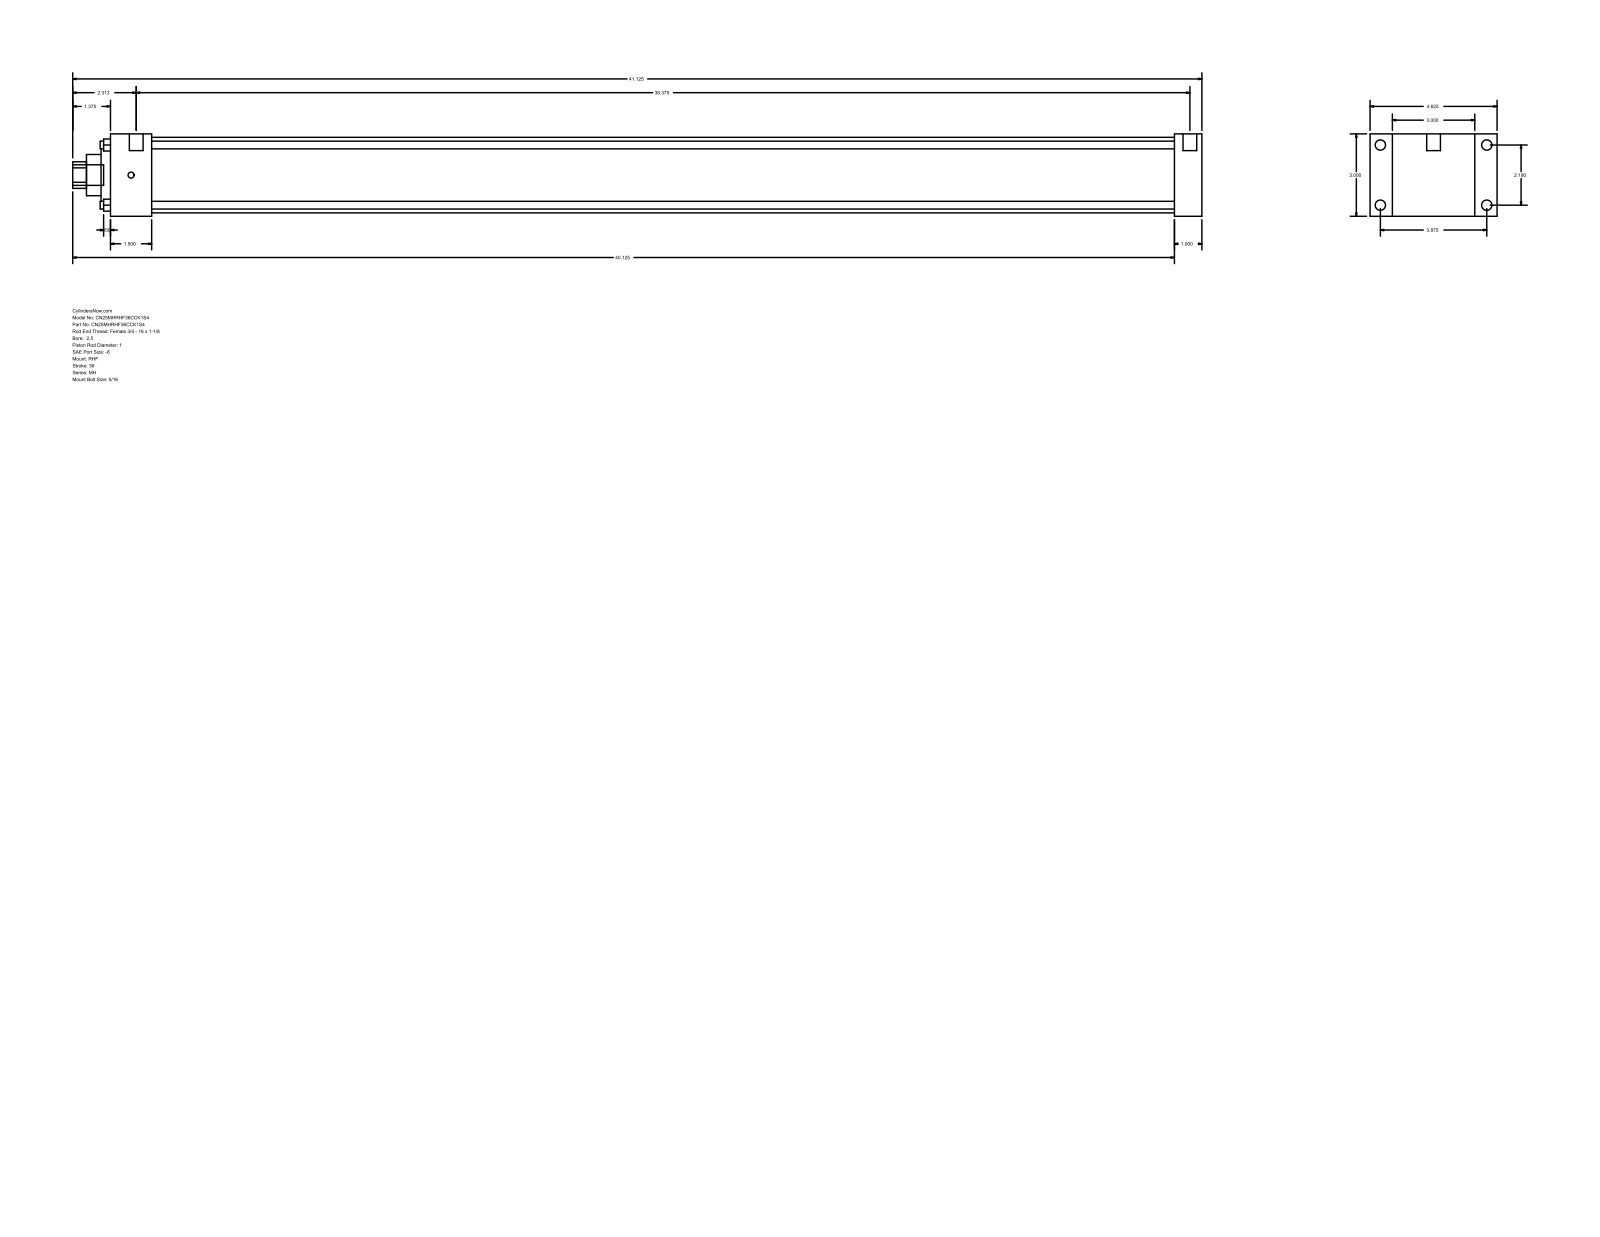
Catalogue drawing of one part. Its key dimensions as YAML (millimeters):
part_name: "MH_RHF__0250_1"
step_written_by: "GSSL Pune (CONFIG_CONTROL_DESIGN)"
units: millimeters
bodies: {solids: 0, faces: 90, planar: 61, cylindrical: 29, other: 0}
overall_size: [1044.58, 117.47, 76.2]
round_holes:
  - {diameter: 7.14, count: 4}
  - {diameter: 25.4, count: 1}
  - {diameter: 38.1, count: 1}
  - {diameter: 60.33, count: 1}
  - {diameter: 69.85, count: 1}
round_bosses_or_shafts:
  - {diameter: 9.53, count: 4}
  - {diameter: 5.56, count: 4}
  - {diameter: 12.7, count: 2}
  - {diameter: 19.05, count: 1}
partial_cylinders:
  - {radius: 12.29, count: 1}
face_to_face_distances: [76.2, 25.41, 20.64, 96.84, 984.25, 1009.66, 117.48, 38.11, 946.14, 971.55]
hole_center_spacings: [39.33, 55.62, 78.66]
